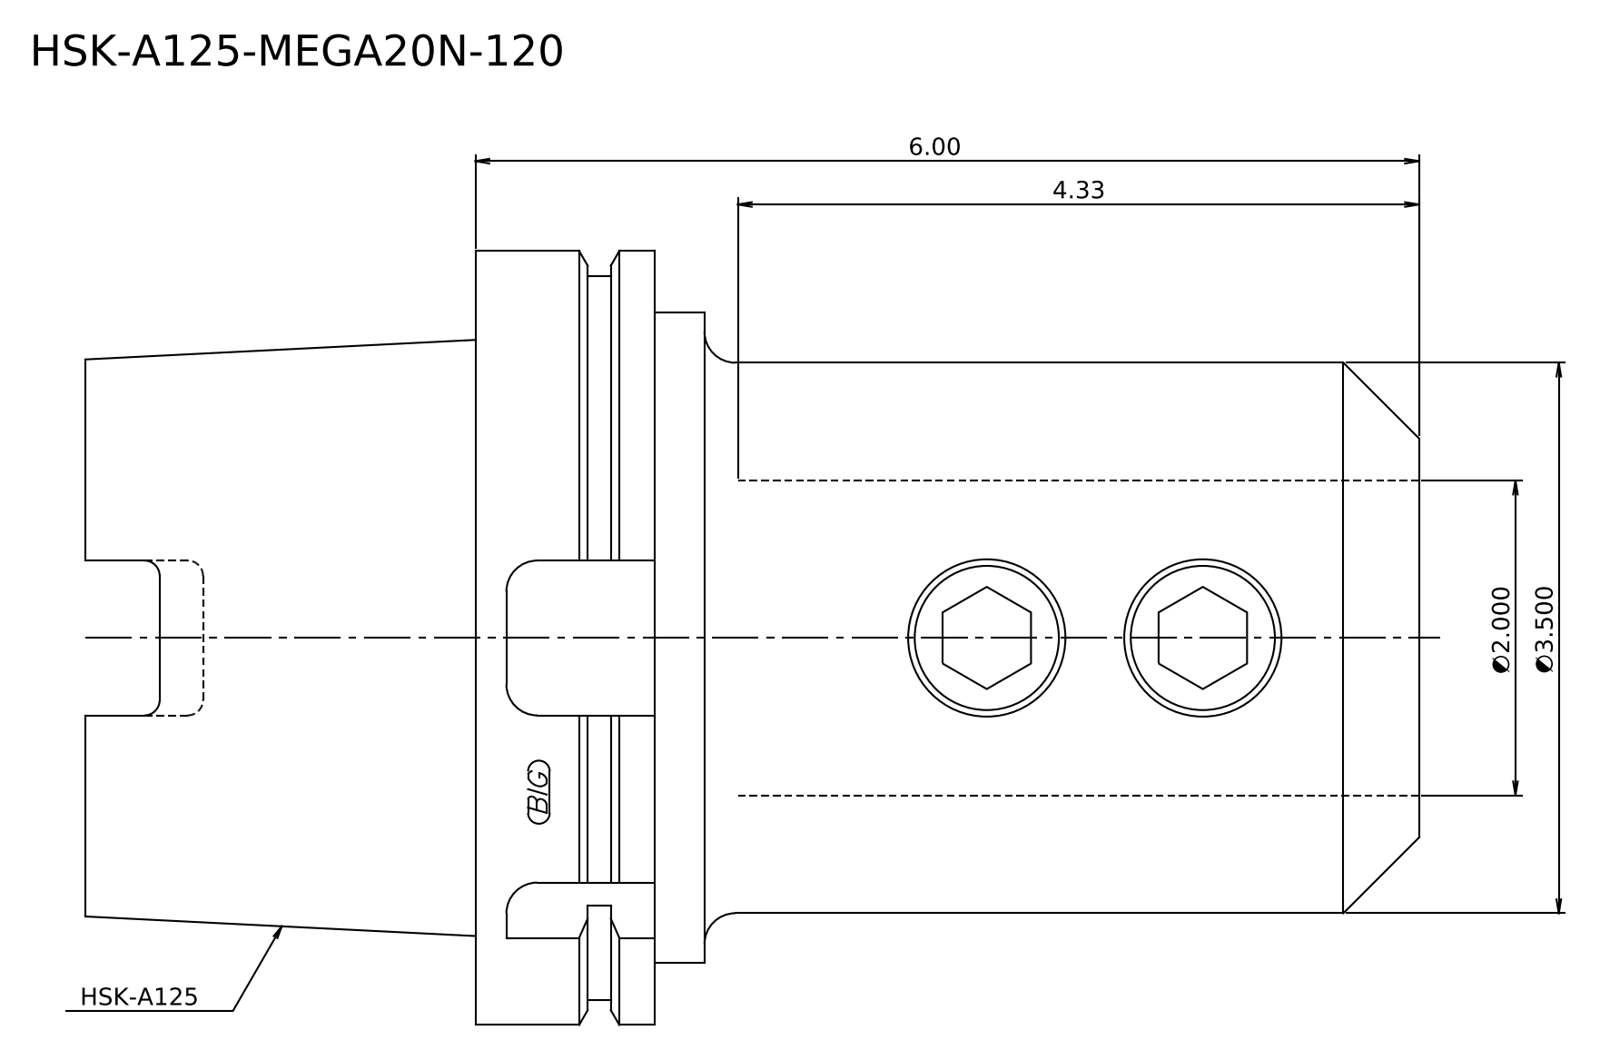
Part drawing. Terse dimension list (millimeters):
written by: Kubotek KeyCreator 2011 V10.0.2 (22737) (automotive_design)
unit: mm
bodies: 1 solid, 17 faces (7 planar, 5 cylindrical, 5 other)
size: 215.4 × 125 × 125
volume: 1 548 000 mm³; area: 87 506 mm²
bosses: 1× ⌀125, 1× ⌀117, 1× ⌀105, 1× ⌀88.9
face distances: 63, 29, 92, 123.4, 152.4, 215.4, 115.4, 8, 37, 100
